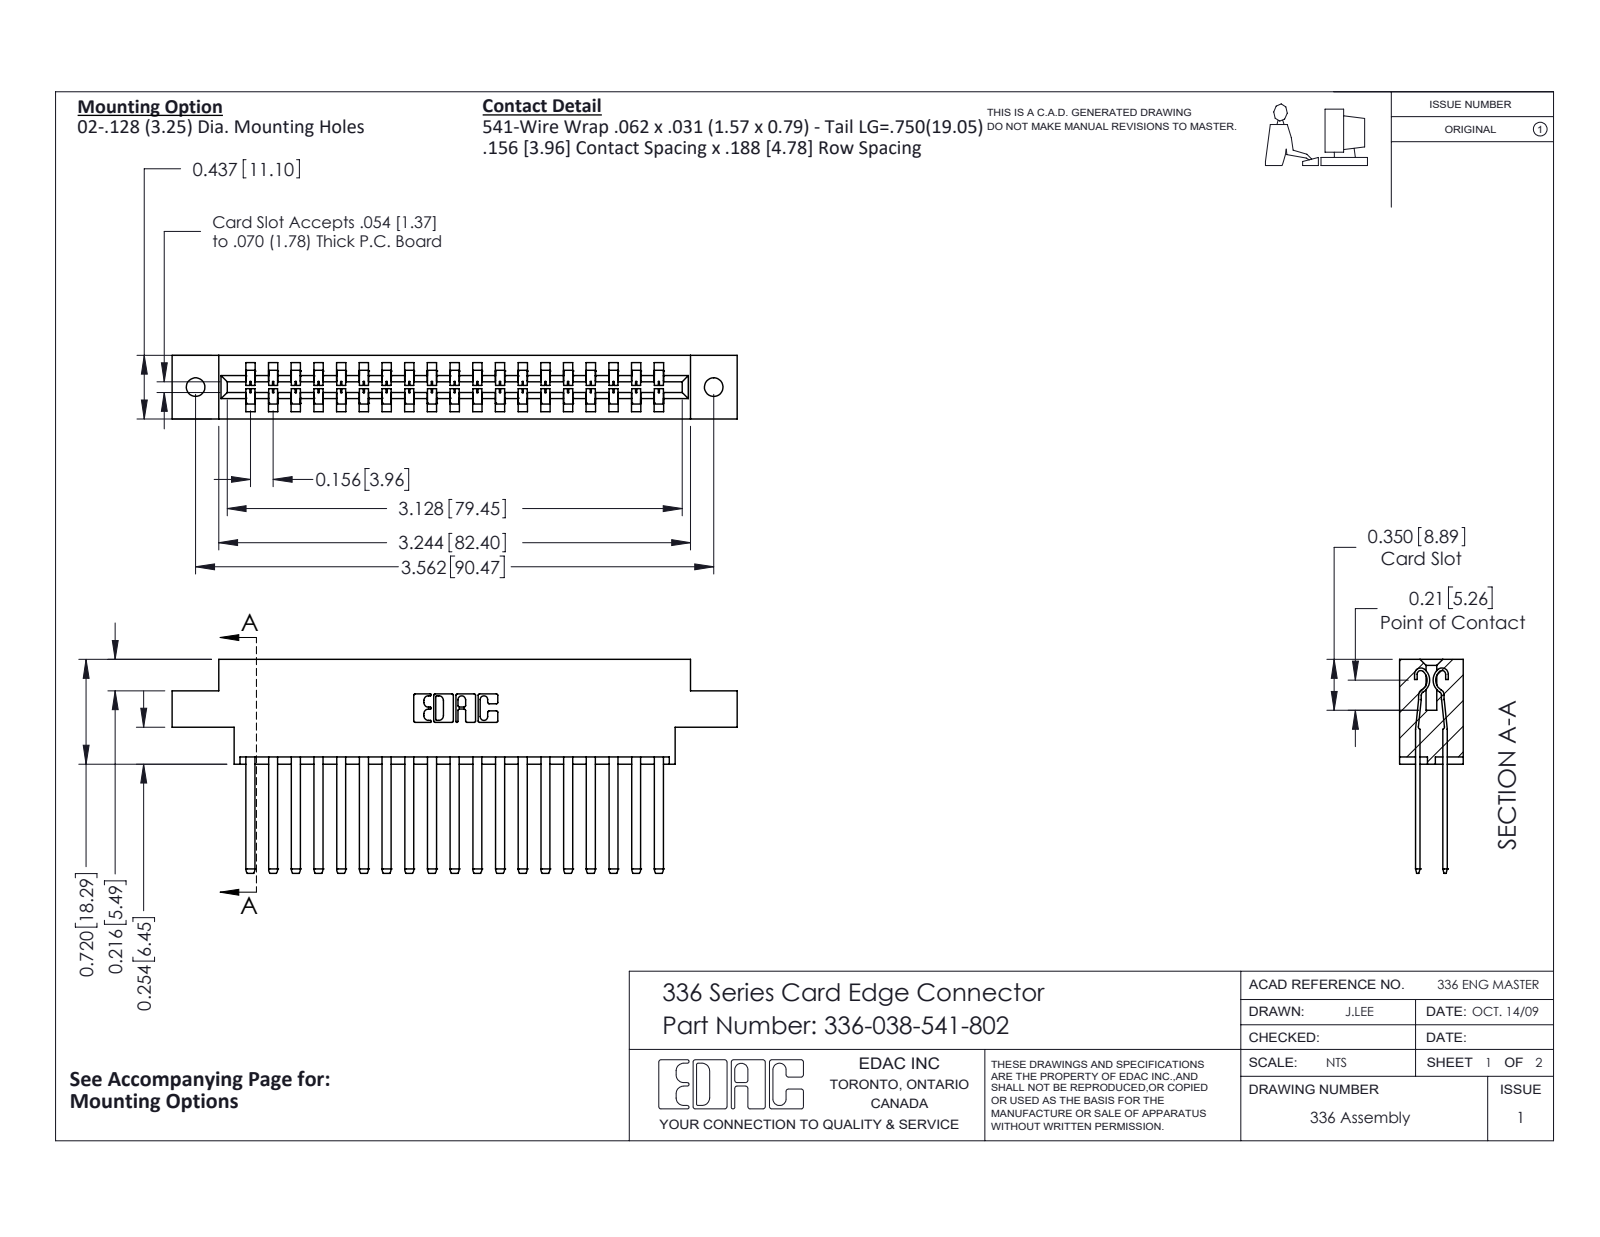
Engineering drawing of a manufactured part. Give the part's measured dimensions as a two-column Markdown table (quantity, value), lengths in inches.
| quantity | value |
| --- | --- |
| part name | 336-290-001_336-290-541; 336-038-541-802; 336 Part_Offset - .128 Dia |
| STEP written by | SolidWorks 2020 (CONFIG_CONTROL_DESIGN) |
| units | inches |
| bodies | 39 solids, 1714 faces (1062 planar, 652 cylindrical, 0 other) |
| overall size | 3.885 × 1.47 × 0.437 |
| volume | 0.873 in³ |
| surface area | 27.52 in² |
| round holes (diameter × count) | 0.128 × 2 |
| partial cylindrical surfaces (radius × count) | 0.004 × 76, 0.056 × 38, 0.01 × 22, 0.007 × 6, 0.031 × 6, 0.022 × 4, 0.04 × 4, 0.026 × 3 |
| main face-to-face distances | 0.188, 0.328, 0.14, 0.297, 0.109, 0.031, 0.437, 0.033, 0.624, 0.181 |
| hole center spacings | 3.562 |
